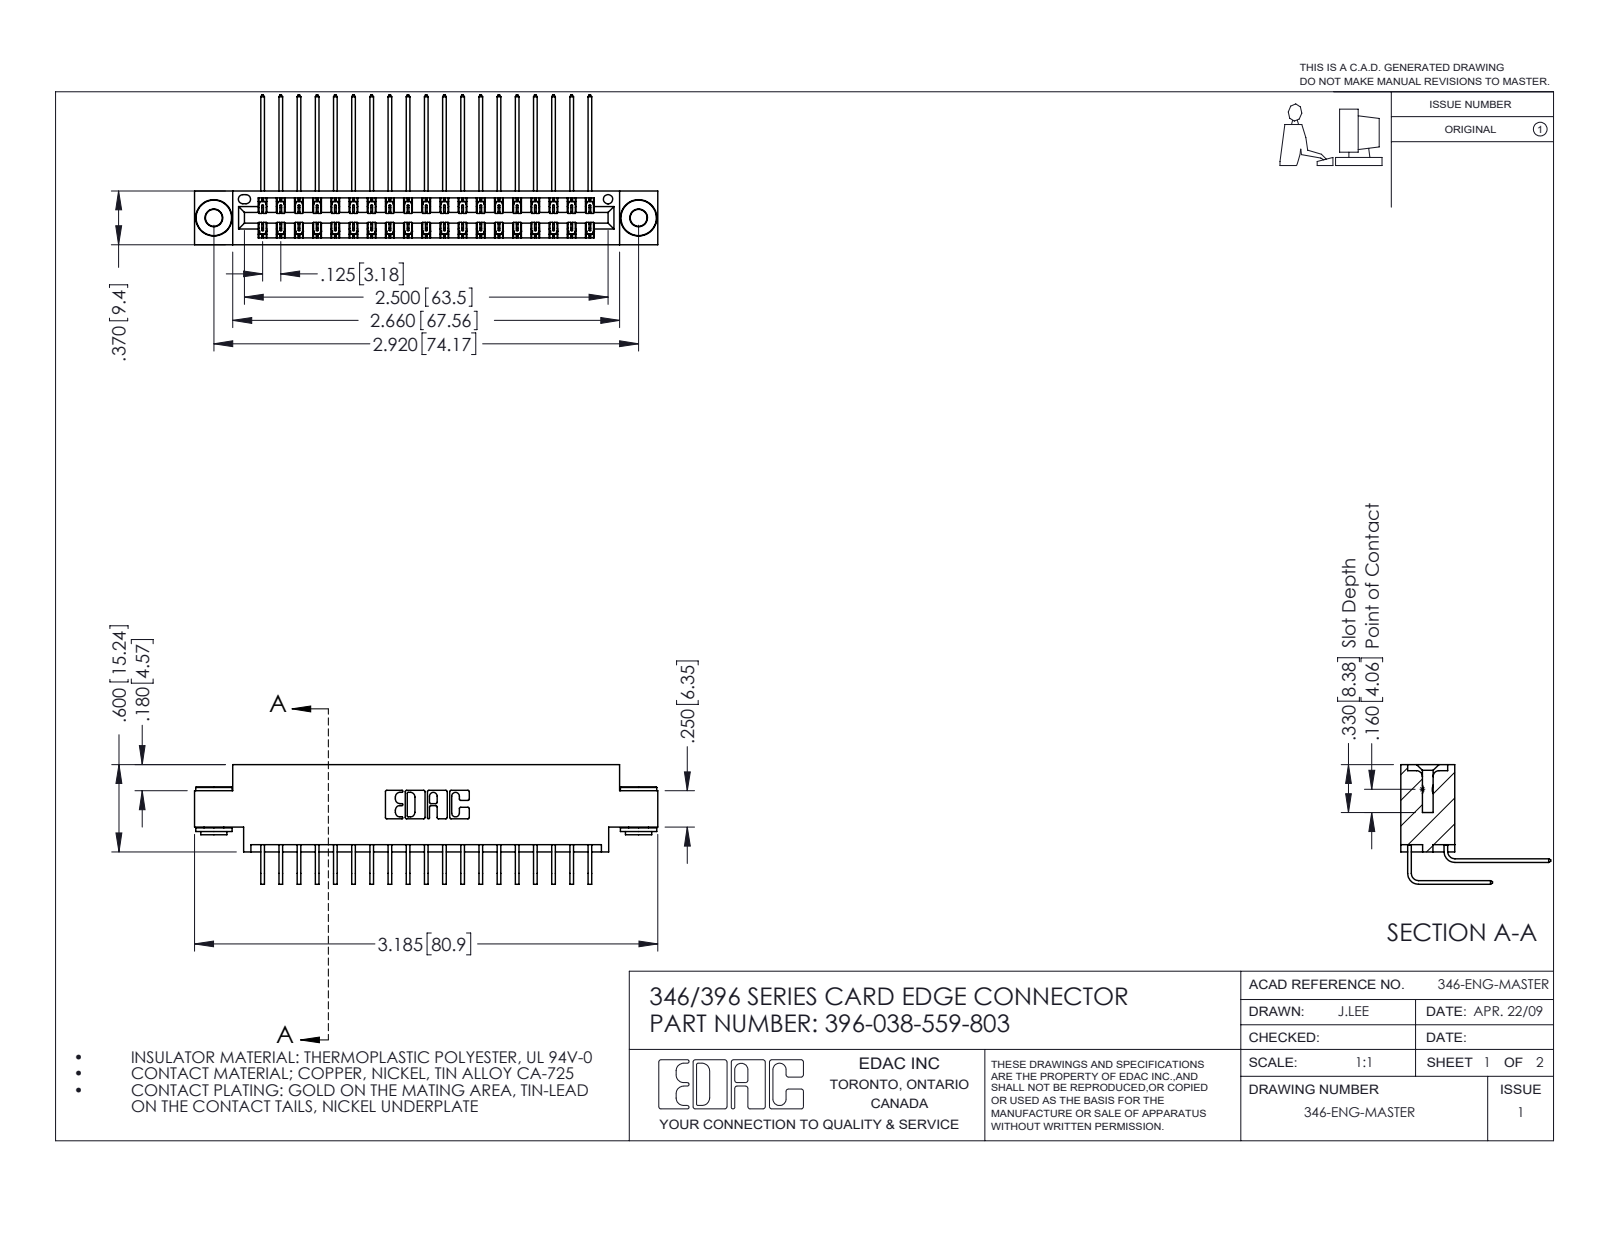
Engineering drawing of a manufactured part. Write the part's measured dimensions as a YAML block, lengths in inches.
part_name: "345-250-002_345-250-002-102; 345-292-001_559 Tail - 2; 345-292-001_558 559 Tail - 1; 396-038-559-803 (+1 more)"
step_written_by: "SolidWorks 2016 (CONFIG_CONTROL_DESIGN)"
units: inches
bodies: {solids: 41, faces: 2216, planar: 1496, cylindrical: 712, other: 8}
overall_size: [3.185, 1.03, 0.823]
volume: 0.476
surface_area: 18.29
round_holes:
  - {diameter: 0.116, count: 2}
  - {diameter: 0.156, count: 2}
  - {diameter: 0.064, count: 1}
round_bosses_or_shafts:
  - {diameter: 0.25, count: 2}
  - {diameter: 0.18, count: 2}
  - {diameter: 0.136, count: 2}
partial_cylinders:
  - {radius: 0.006, count: 57}
  - {radius: 0.01, count: 22}
  - {radius: 0.007, count: 6}
  - {radius: 0.031, count: 6}
  - {radius: 0.026, count: 3}
  - {radius: 0.014, count: 2}
  - {radius: 0.022, count: 2}
  - {radius: 0.024, count: 2}
face_to_face_distances: [0.048, 0.322, 0.37, 0.025, 0.25, 0.072, 0.298, 0.275, 0.15, 0.148]
hole_center_spacings: [0.246, 2.713, 2.92]
